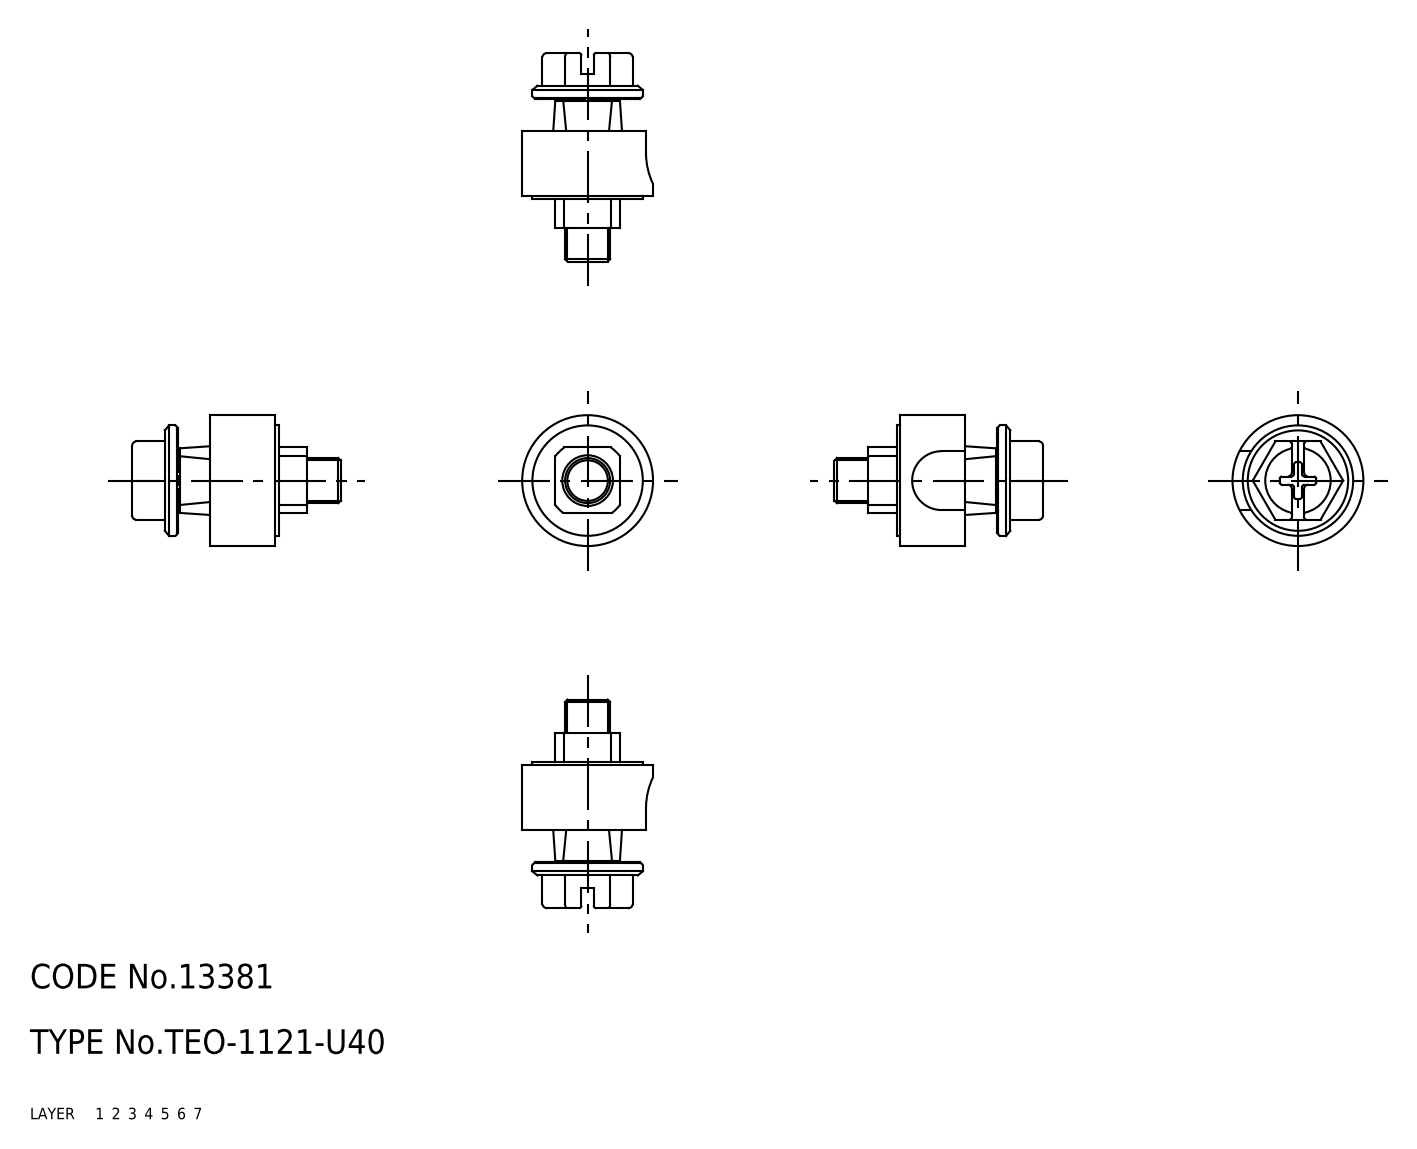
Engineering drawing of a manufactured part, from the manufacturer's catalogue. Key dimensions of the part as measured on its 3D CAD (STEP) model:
Part name (STEP PRODUCT): screw; adapter; TEO_1121_U40_7766_36
STEP written by: CADfix (AUTOMOTIVE_DESIGN)
Units: millimetres
Bodies: 2 solids, 143 faces (0 planar, 0 cylindrical, 143 other)
Overall size (bounding box): 25.5 × 16 × 16
Volume: 2 508 mm³ · Surface area: 2 150 mm²
